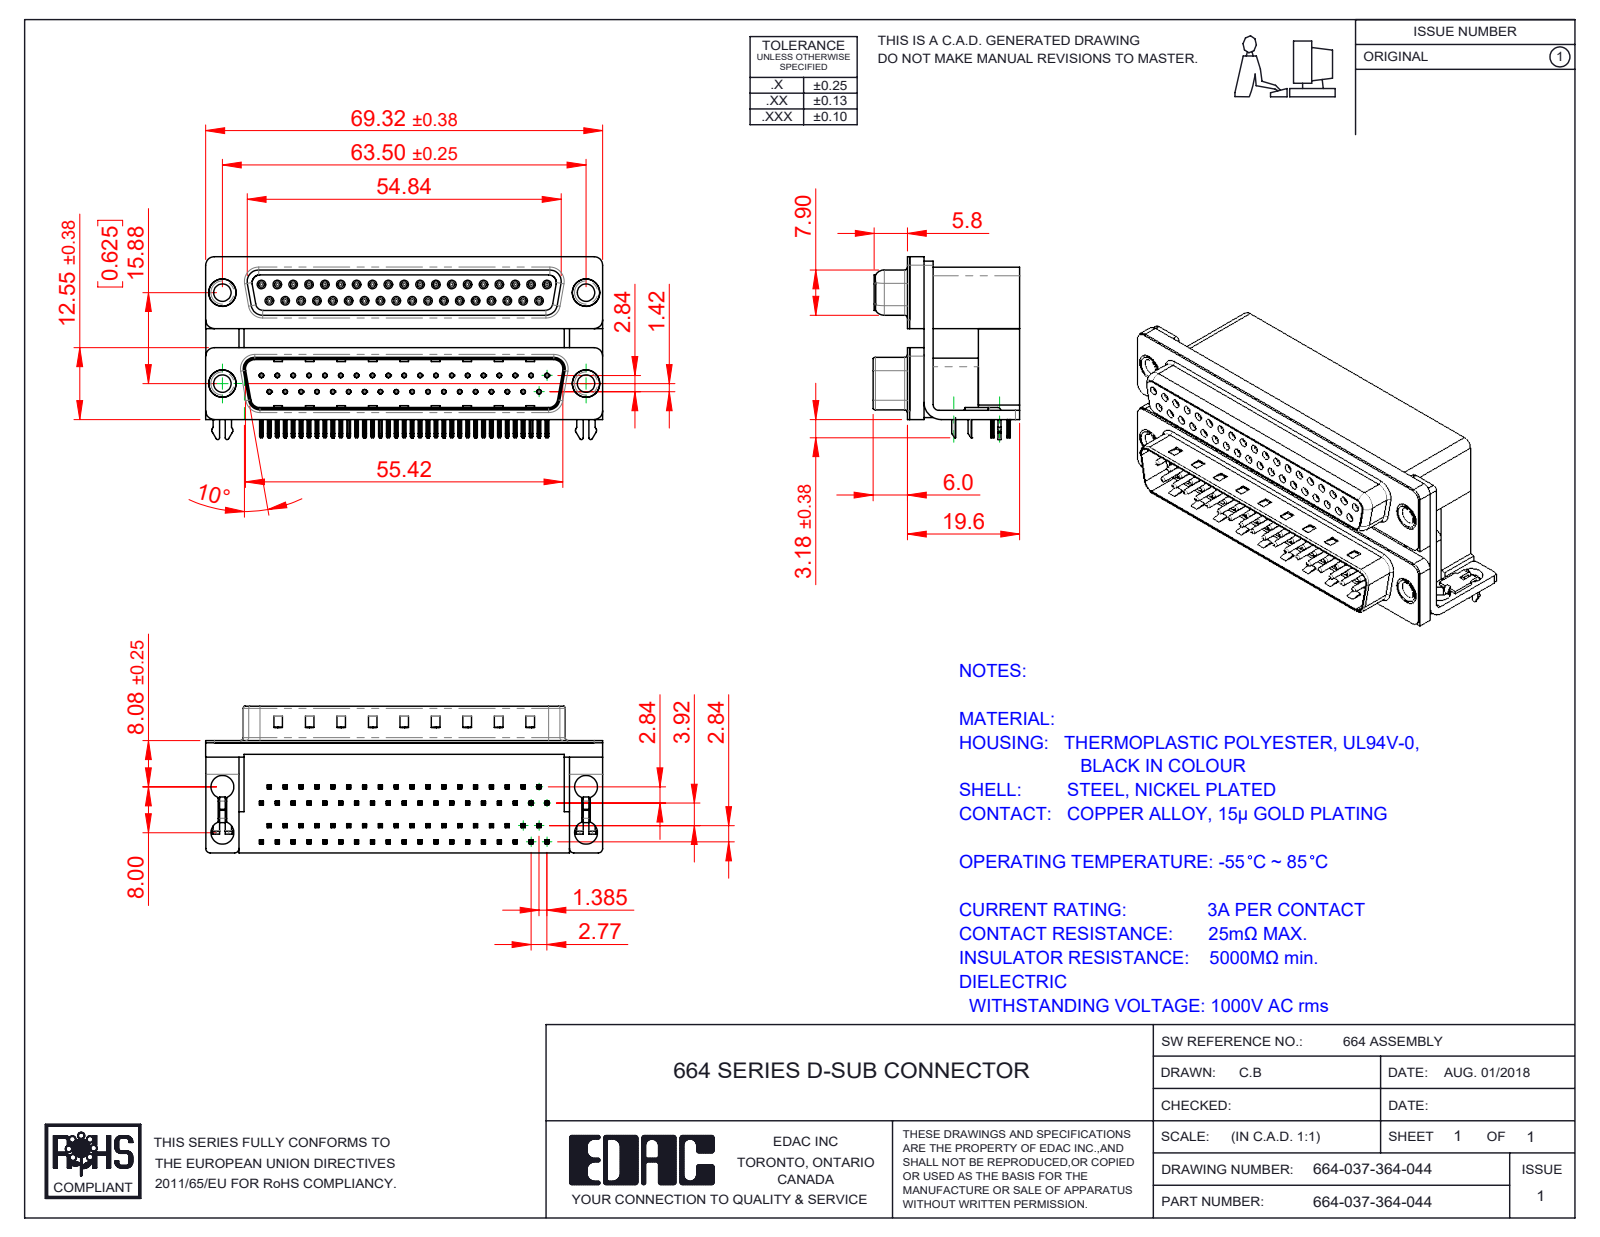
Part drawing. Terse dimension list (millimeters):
name: 664 Shell Receptacle_37 Contacts; 664 Thru Hole Rivet; 664 Contact Top Lower; 664 Housing Upper_37 Contacts L (+8 more)
written by: SolidWorks 2020 (CONFIG_CONTROL_DESIGN)
unit: mm
bodies: 87 solids, 8969 faces (4819 planar, 2171 cylindrical, 1979 other)
size: 69.32 × 31.93 × 25.6
volume: 29 759 mm³; area: 31 558 mm²
holes: 74× ⌀0.8, 37× ⌀0.35, 37× ⌀0.9, 8× ⌀4, 4× ⌀3.05, 4× ⌀3.5, 4× ⌀4.8, 4× ⌀5
bosses: 37× ⌀1.2, 37× ⌀0.75, 4× ⌀4.9, 4× ⌀4.75, 4× ⌀3.85
rounds: 297× R0.1, 154× R0.25, 148× R0.15, 74× R0.12, 74× R0.35, 37× R0.34, 18× R0.28, 16× R0.5
face distances: 0.4, 19.2, 7.2, 12, 2.19, 15.52, 2.84, 26.22, 10.7, 13.33
hole spacings: 2.77, 5.54, 3.16, 8.31, 11.08, 13.85, 16.62, 19.39
